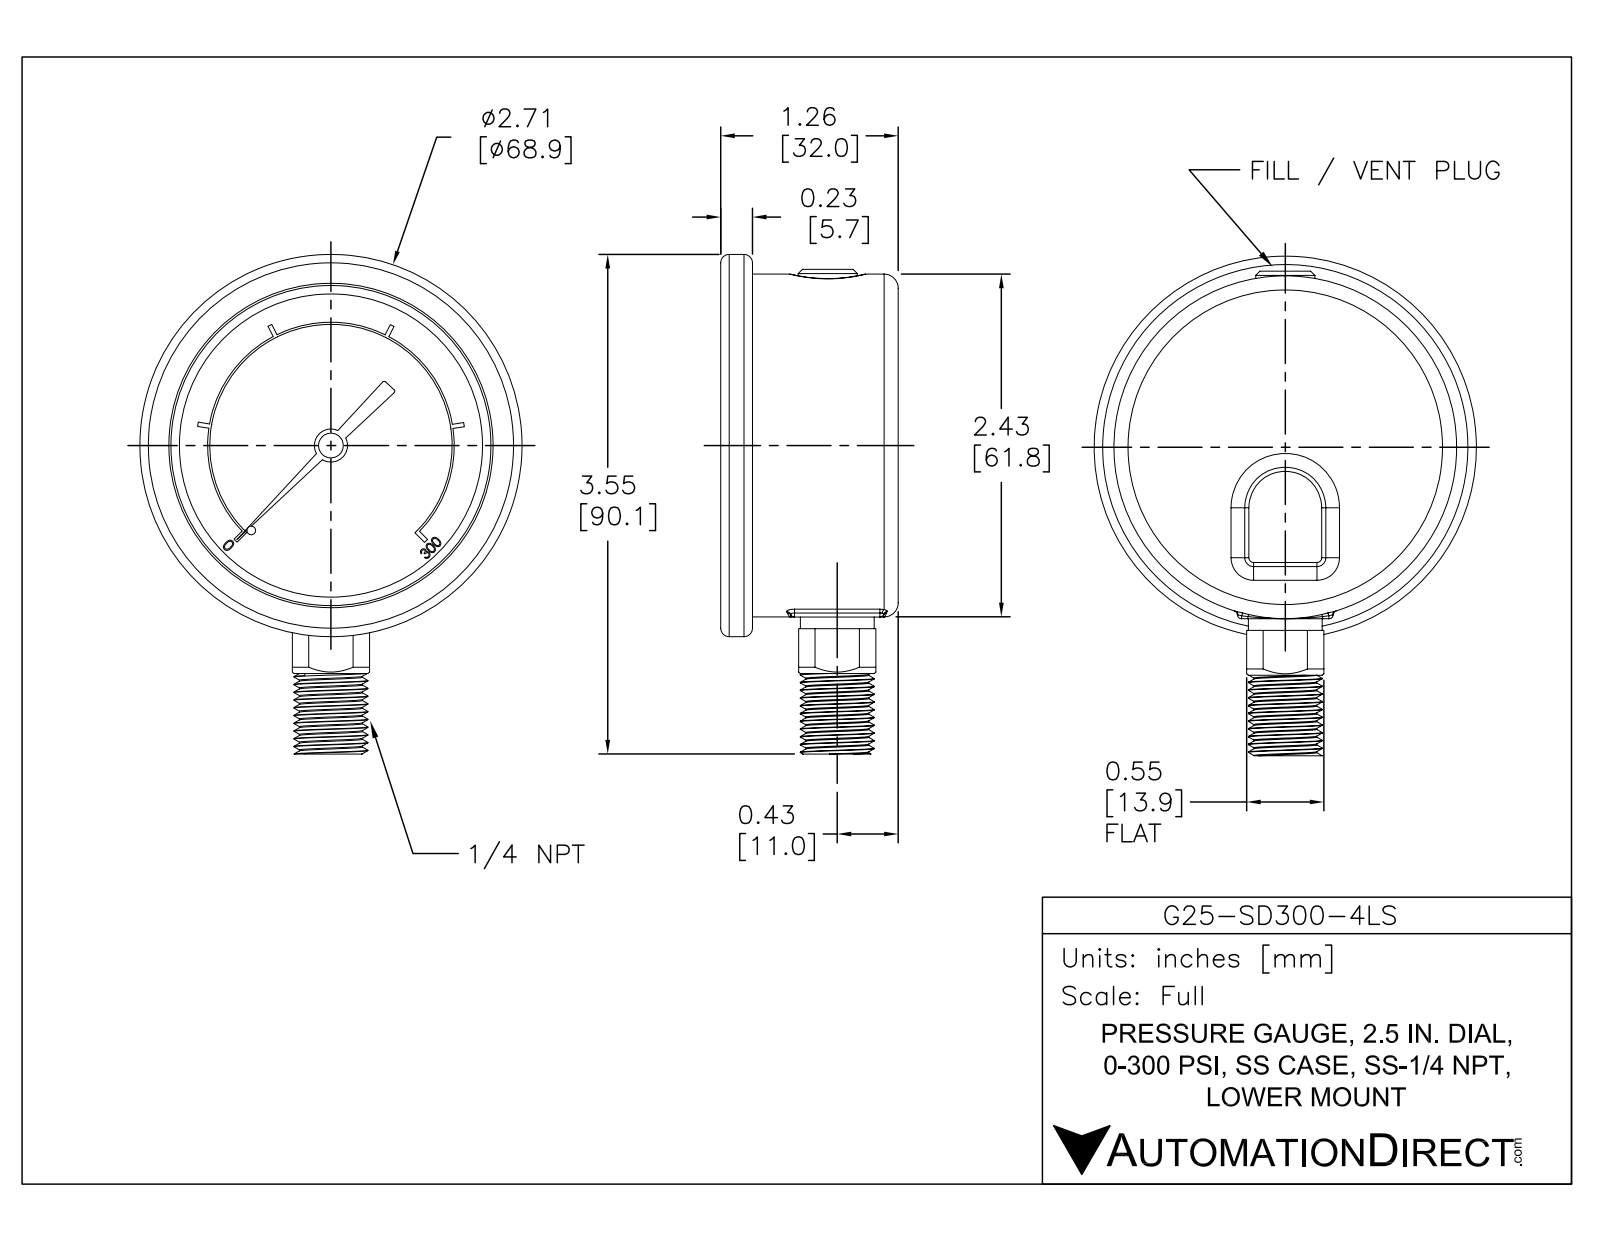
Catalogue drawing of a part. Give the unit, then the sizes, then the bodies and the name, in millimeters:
Units: millimetres
Overall size (bounding box): 90.1 × 68.9 × 32
Round holes (diameter × count): ⌀0.7 ×1, ⌀1.8 ×1, ⌀3 ×1, ⌀57.7 ×1
Round bosses / shafts (diameter × count): ⌀68.9 ×1, ⌀61.8 ×1, ⌀13.3 ×1, ⌀10.7 ×1, ⌀6 ×1, ⌀4.5 ×1, ⌀3.6 ×1, ⌀1 ×1
Partial cylindrical surfaces — rounded edges, fillets, slot ends (radius × count): R0.8 ×9, R2.5 ×3, R0.4 ×2, R8 ×1, R21.8 ×1, R22.2 ×1
Main face-to-face distances: 25.7, 32, 6.4, 26.3, 0.6, 5.7, 2.5, 23.1, 23.7, 29.5
Hole centre spacings: 1.7
Volume: 86 410 mm³ · Surface area: 15 920 mm²
Bodies: 1 solid, 354 faces (192 planar, 85 cylindrical, 77 other)
Part name (STEP PRODUCT): G25-SD300-4LS
STEP written by: SolidWorks 2021 (AUTOMOTIVE_DESIGN)
